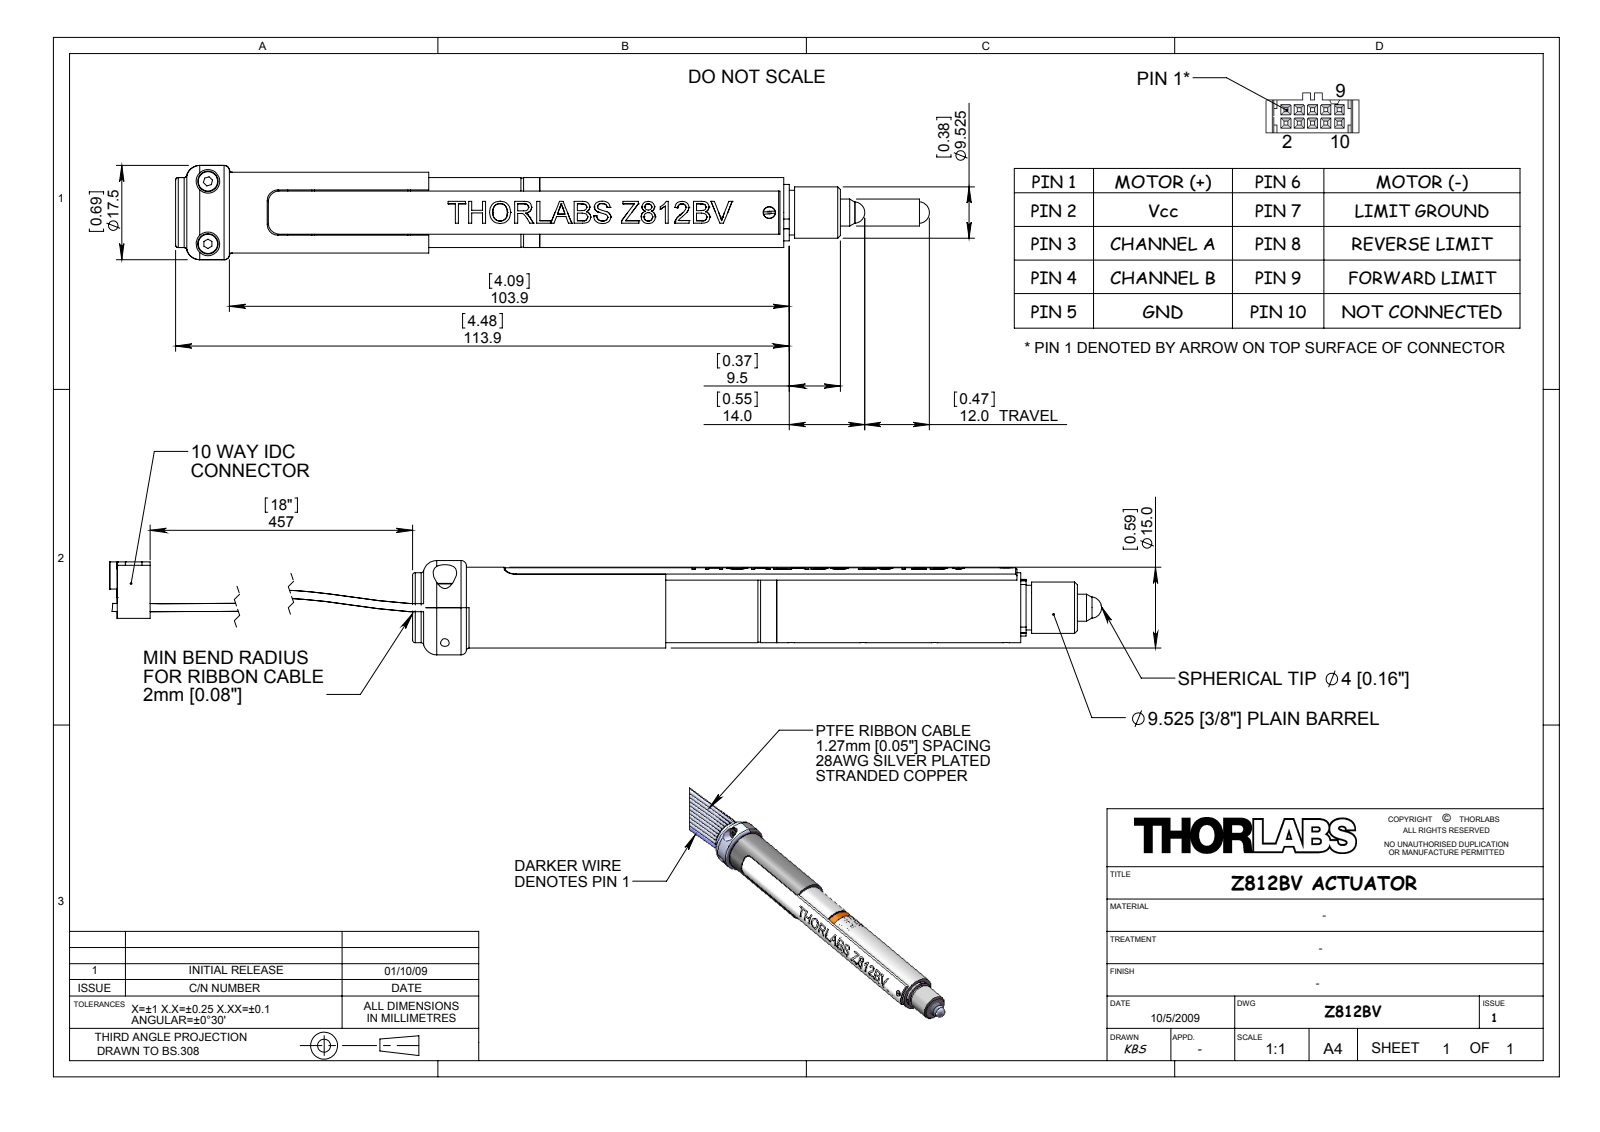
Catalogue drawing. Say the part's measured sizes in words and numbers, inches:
The part is named "Z812BV". Its 3-D file was written by "SolidWorks 2007 (AUTOMOTIVE_DESIGN)". It is 0 solids with 190 faces: 47 planar, 105 cylindrical and 38 other. Overall it measures 5.036 by 0.689 by 0.689 inches. Round holes: 4 of diameter 0.047, 2 of diameter 0.063, 2 of diameter 0.173. Round bosses or shafts: 2 of diameter 0.15, 1 of diameter 0.689, 1 of diameter 0.591, 1 of diameter 0.512, 1 of diameter 0.504, 1 of diameter 0.472, 1 of diameter 0.413, 1 of diameter 0.375. Partial cylindrical surfaces (rounded edges, fillets, slot ends): 4 of radius 0.079, 2 of radius 0.059, 1 of radius 0.246, 1 of radius 0.258, 1 of radius 0.291, 1 of radius 0.292. The main face-to-face distances are 2.661, 0.315, 0.043, 0.394, 2.268, 0.039, 4.445, 4.051, 1.783, 4.858. The hole center spacings are 0.524, 1.047, 2.542, 3.064, 3.586, 4.109, 0.457, 1.571.
